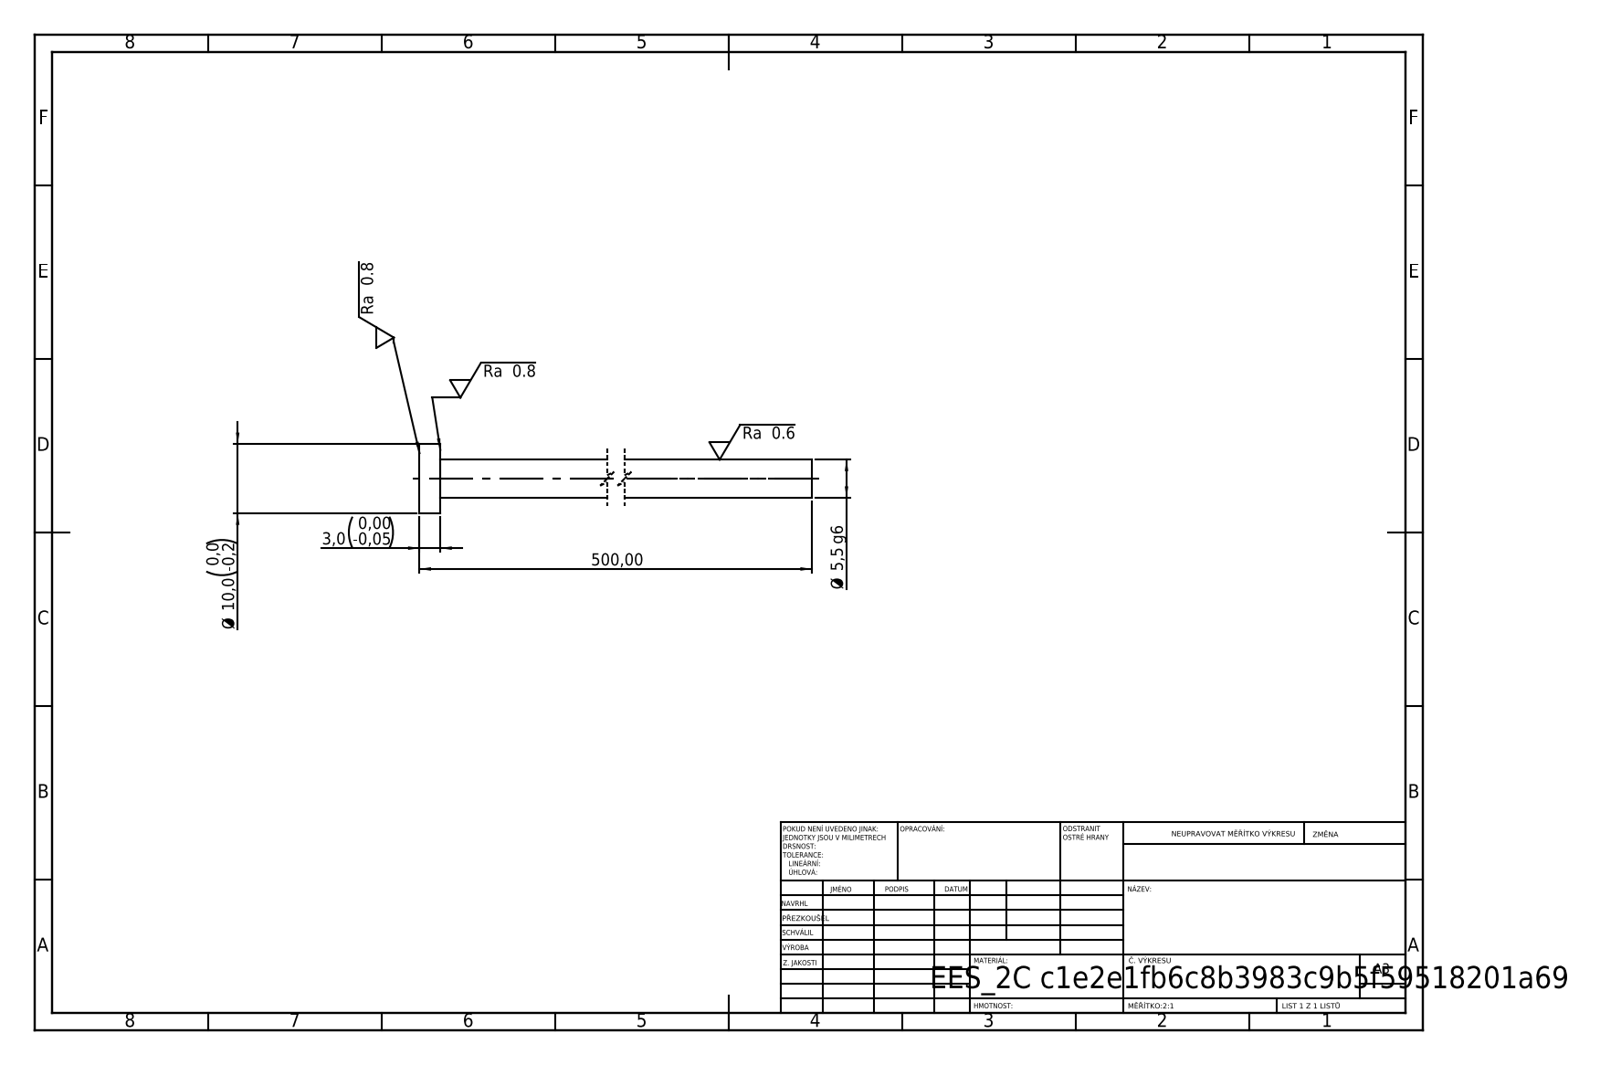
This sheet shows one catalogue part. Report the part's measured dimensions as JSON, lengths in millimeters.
{"step_written_by": "SolidWorks 2019 (CONFIG_CONTROL_DESIGN)", "units": "millimeters", "bodies": {"solids": 1, "faces": 7, "planar": 3, "cylindrical": 4, "other": 0}, "overall_size": [500, 10, 10], "volume_mm3": 12043, "surface_area_mm2": 8839, "round_bosses_or_shafts": [[10, 1], [5.5, 1]], "face_to_face_distances": [3, 500, 497]}
